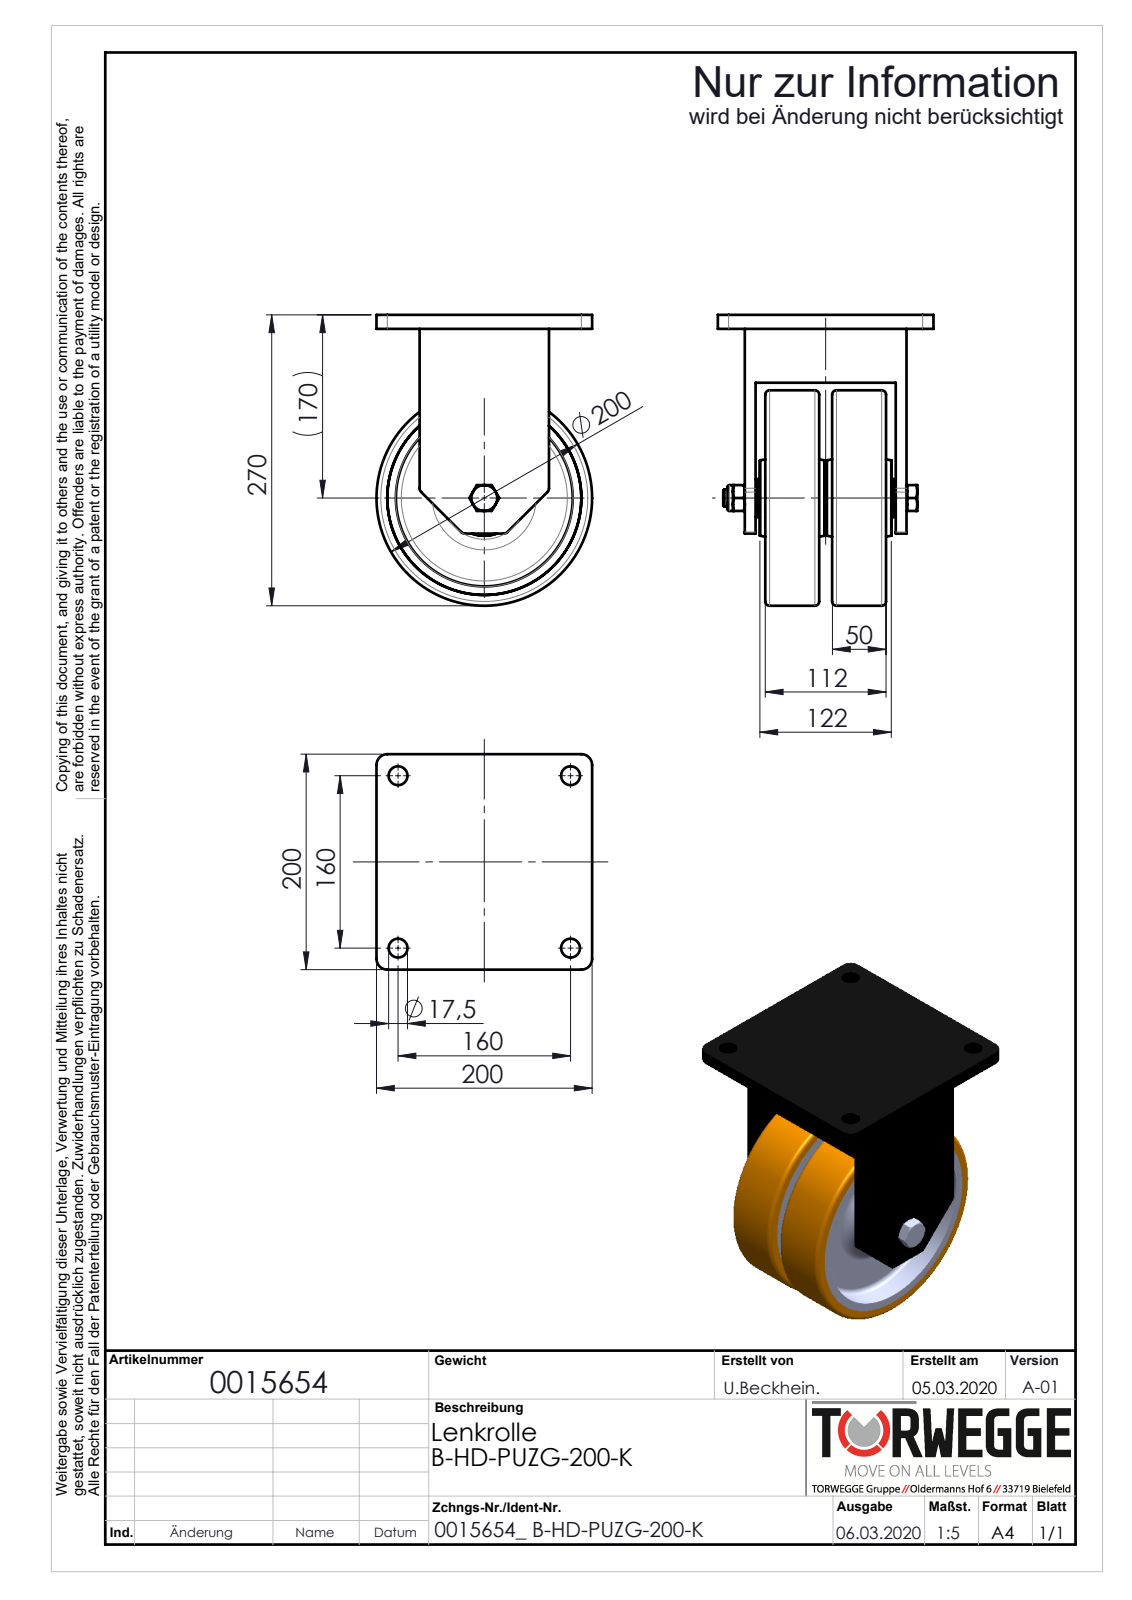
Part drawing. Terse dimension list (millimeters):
name: 0015654_B-HD-PUZG-200-K_(A-01)
written by: SolidWorks 2018 (AUTOMOTIVE_DESIGN)
unit: mm
bodies: 0 solids, 317 faces (87 planar, 116 cylindrical, 114 other)
size: 270 × 200 × 200
holes: 4× ⌀17.5, 1× ⌀14, 1× ⌀16, 1× ⌀16.5, 1× ⌀18.29, 1× ⌀20, 1× ⌀25, 1× ⌀26, 1× ⌀39.8, 1× ⌀164, 1× ⌀180
bosses: 1× ⌀200, 1× ⌀47, 1× ⌀35, 1× ⌀32.2, 1× ⌀24
rounds: 4× R5, 4× R10
face distances: 10, 62, 140, 13, 22, 28, 99, 150, 37, 41
hole spacings: 160, 226.27
